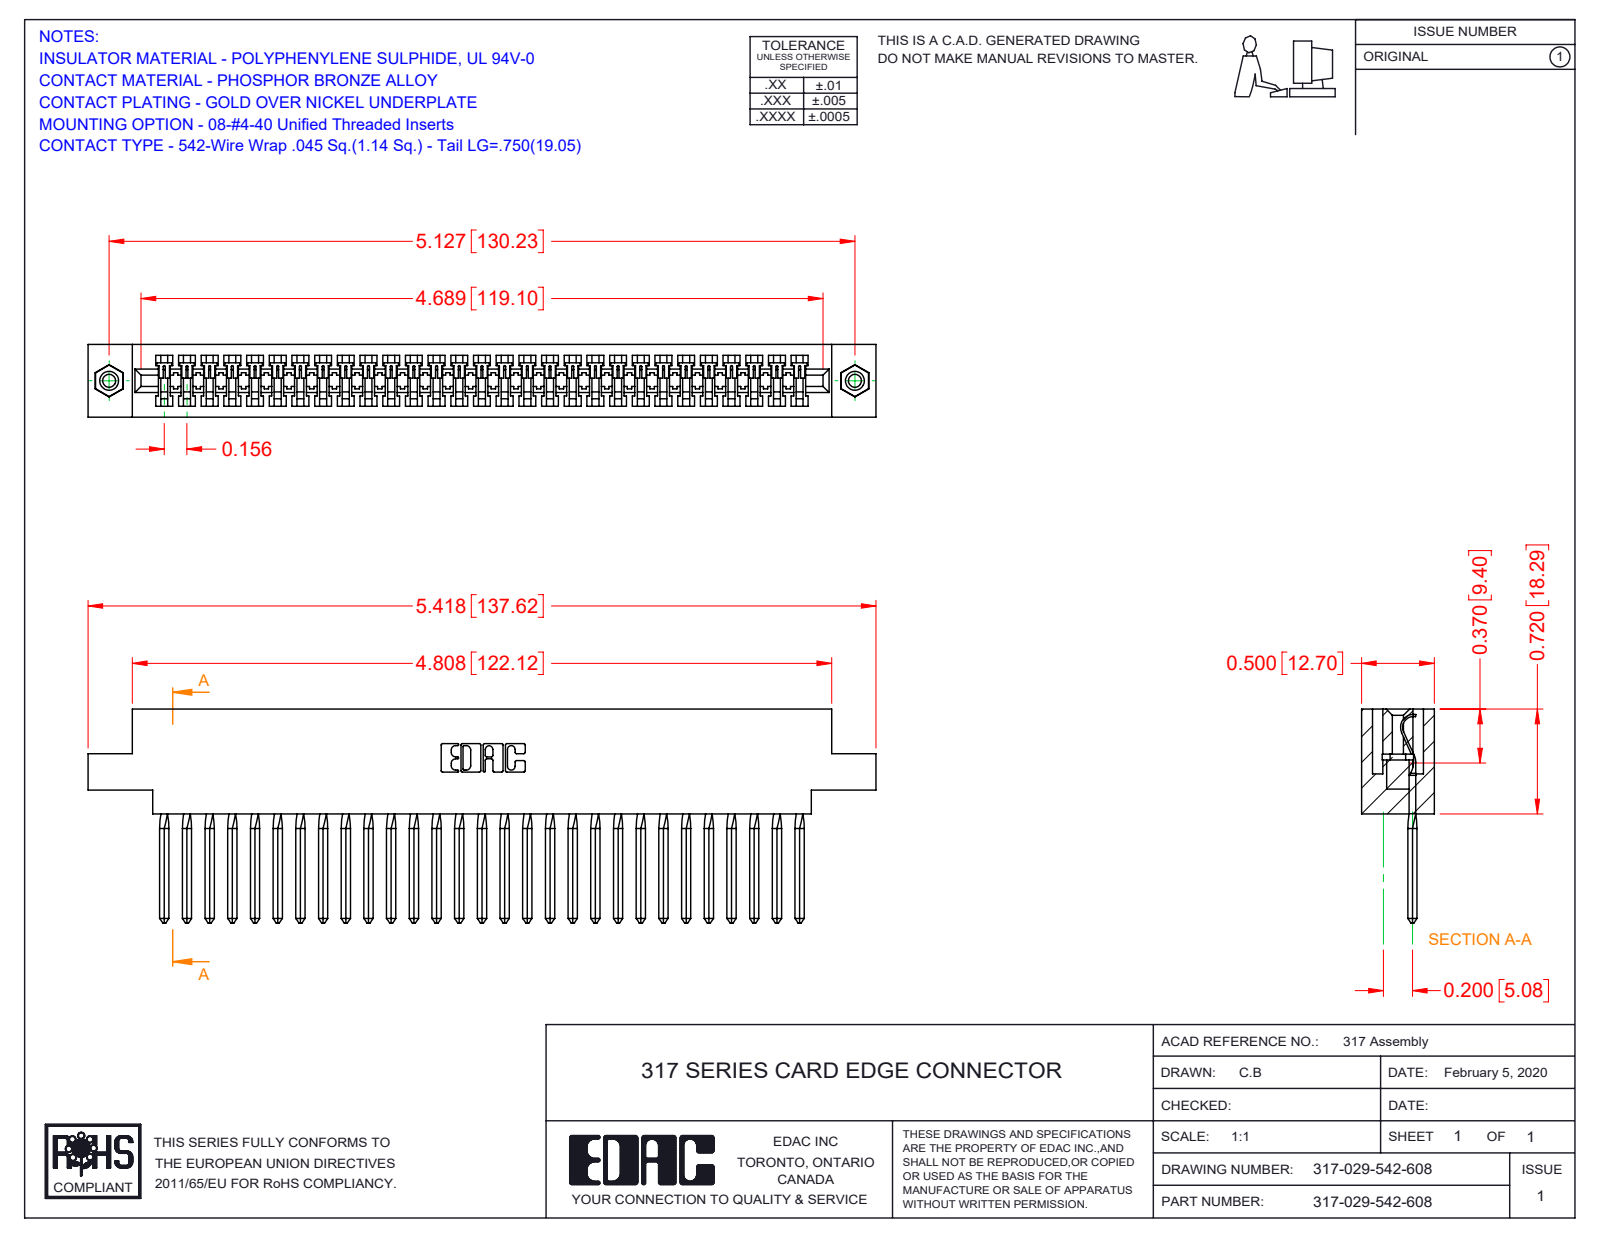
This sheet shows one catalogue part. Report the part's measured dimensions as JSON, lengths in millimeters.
{"part_name": "317-290-003_542; 317-029-542-608; 345-250-001_345-250-003-102; 317 Part_.156 Dia - TI", "step_written_by": "SolidWorks 2016 (CONFIG_CONTROL_DESIGN)", "units": "millimeters", "bodies": {"solids": 32, "faces": 2337, "planar": 1946, "cylindrical": 259, "other": 132}, "overall_size": [137.6, 37.3, 12.7], "volume_mm3": 20910, "surface_area_mm2": 25230, "round_holes": [[2.3, 2], [3.2, 2], [4, 2]], "round_bosses_or_shafts": [[3.9, 2]], "partial_cylinders_radius": [[0.2, 58], [0.3, 22], [0.2, 6], [0.8, 6], [0.7, 3], [1.9, 1], [2.3, 1], [2.5, 1]], "face_to_face_distances": [12.7, 1.9, 10.8, 8.9, 2.8, 3.5, 18.3, 5.4, 7.3, 5.4], "hole_center_spacings": [130.2]}
